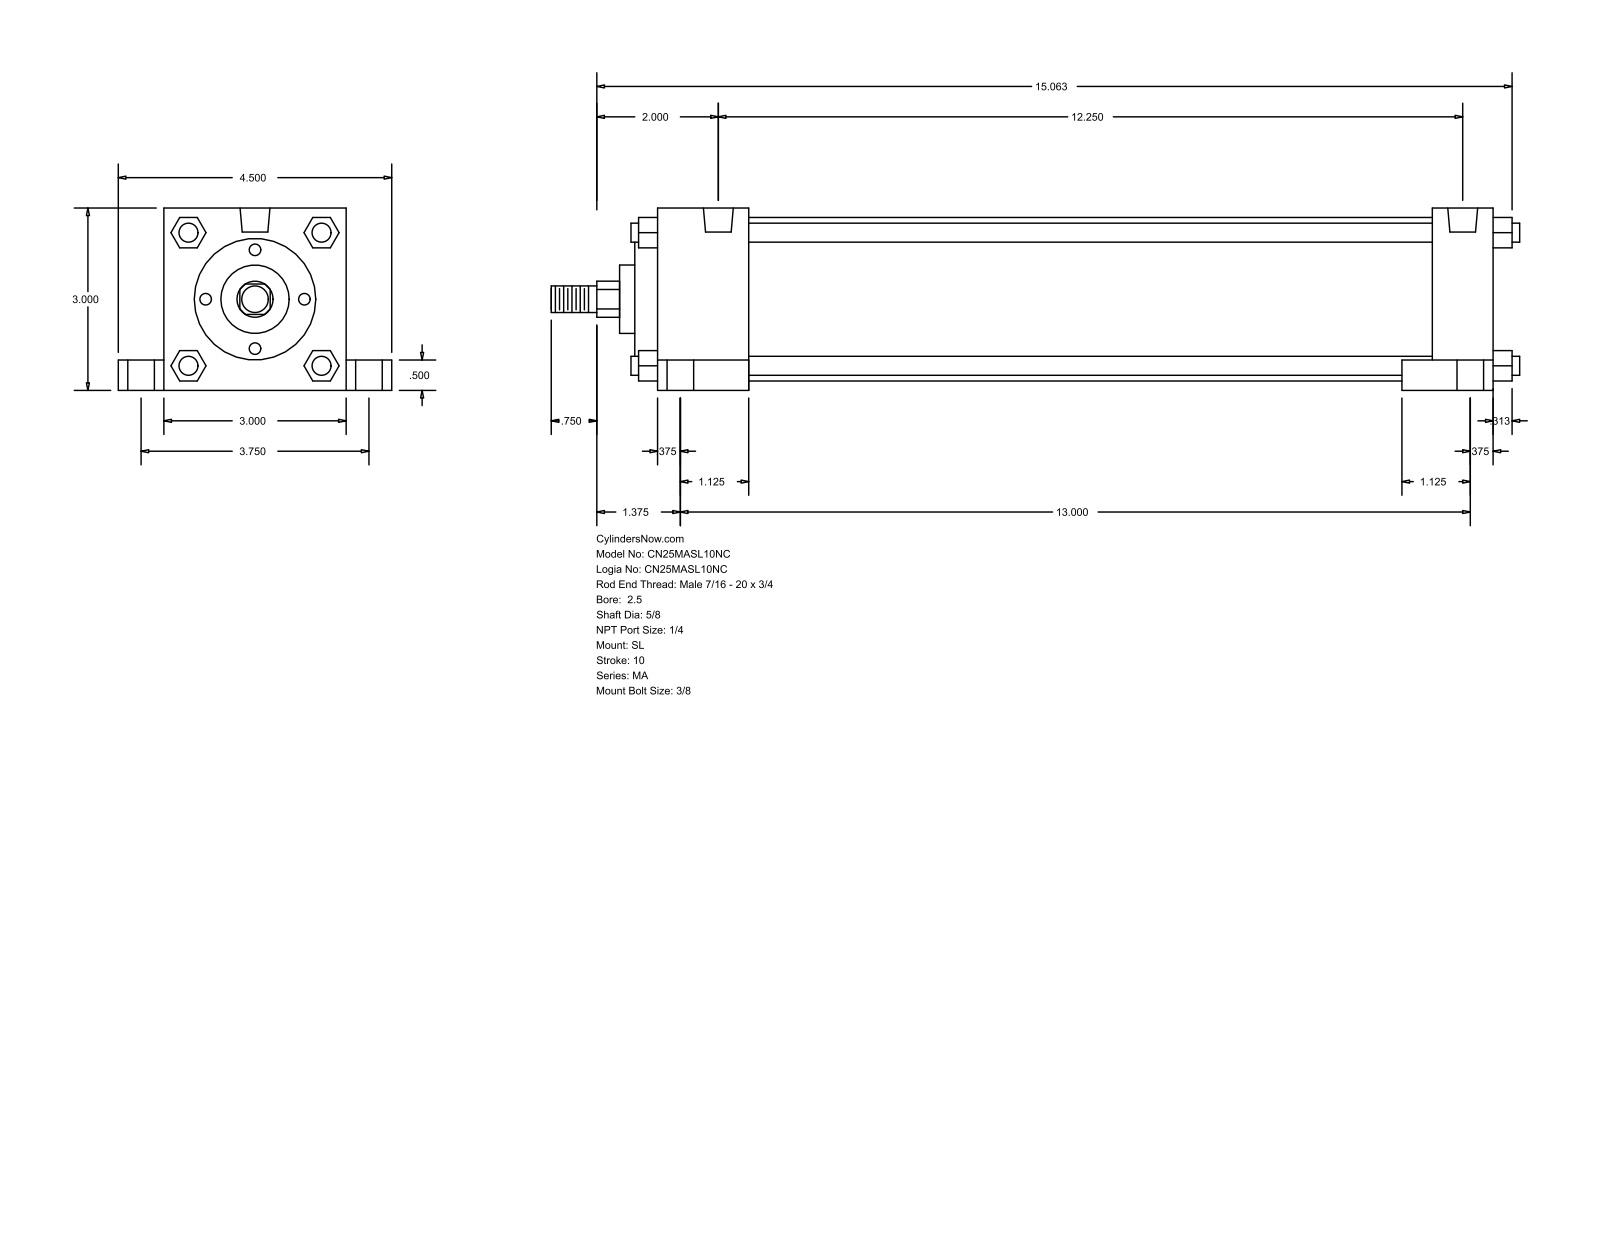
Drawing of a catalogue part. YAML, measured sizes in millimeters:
part_name: "MA_SL__0250_0.625"
step_written_by: "GSSL Pune (CONFIG_CONTROL_DESIGN)"
units: millimeters
bodies: {solids: 0, faces: 150, planar: 113, cylindrical: 37, other: 0}
overall_size: [404.81, 114.3, 76.2]
round_holes:
  - {diameter: 7.94, count: 4}
  - {diameter: 11.11, count: 4}
  - {diameter: 17.46, count: 4}
  - {diameter: 12.49, count: 2}
round_bosses_or_shafts:
  - {diameter: 7.94, count: 4}
  - {diameter: 68.33, count: 1}
  - {diameter: 50.8, count: 1}
  - {diameter: 28.57, count: 1}
  - {diameter: 15.88, count: 1}
  - {diameter: 11.11, count: 1}
partial_cylinders:
  - {radius: 7.54, count: 1}
face_to_face_distances: [76.2, 349.25, 12.7, 285.75, 25.4, 38.1, 311.15, 323.85, 19.05, 63.5]
hole_center_spacings: [47.73, 50.2, 95.24, 311.15, 317.91, 330.2, 330.48, 343.66]
